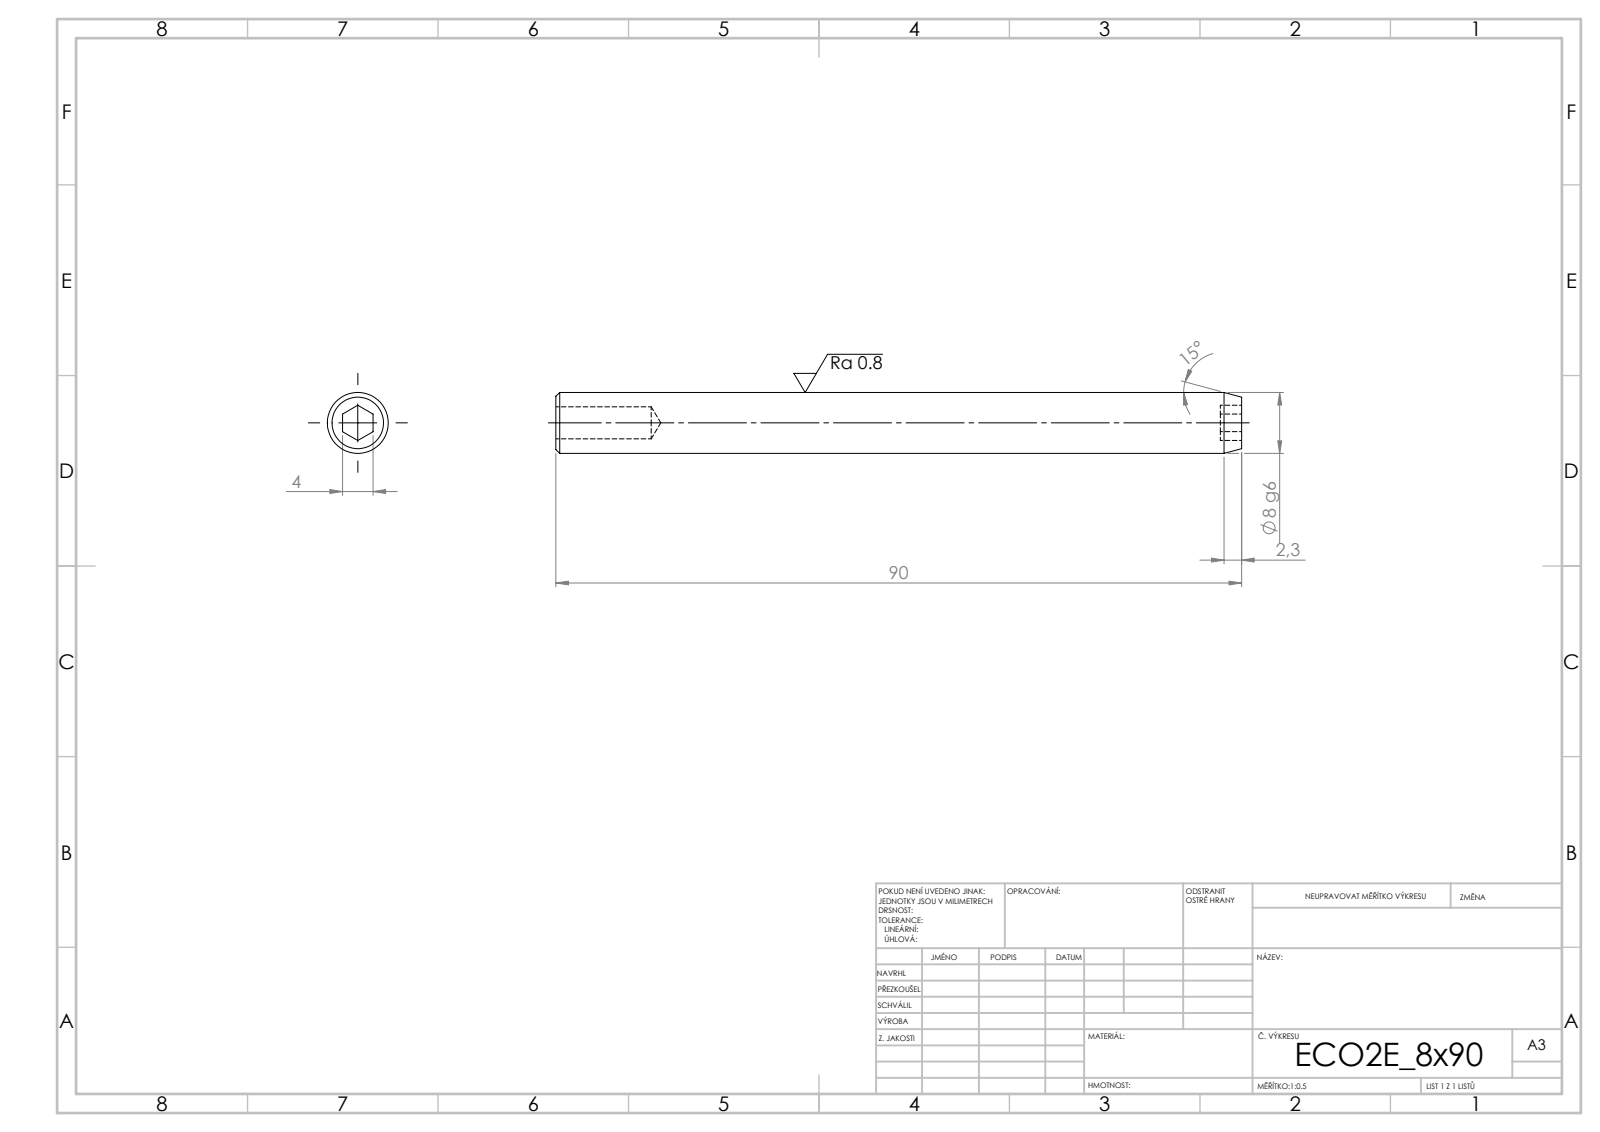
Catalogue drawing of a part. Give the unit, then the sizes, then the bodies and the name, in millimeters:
Units: millimetres
Overall size (bounding box): 90 × 8 × 8
Round holes (diameter × count): ⌀4.2 ×1
Round bosses / shafts (diameter × count): ⌀8 ×1
Main face-to-face distances: 90, 4, 2.8, 87.2
Volume: 4 286 mm³ · Surface area: 2 544 mm²
Bodies: 1 solid, 19 faces (9 planar, 4 cylindrical, 6 other)
STEP written by: SolidWorks 2019 (CONFIG_CONTROL_DESIGN)
